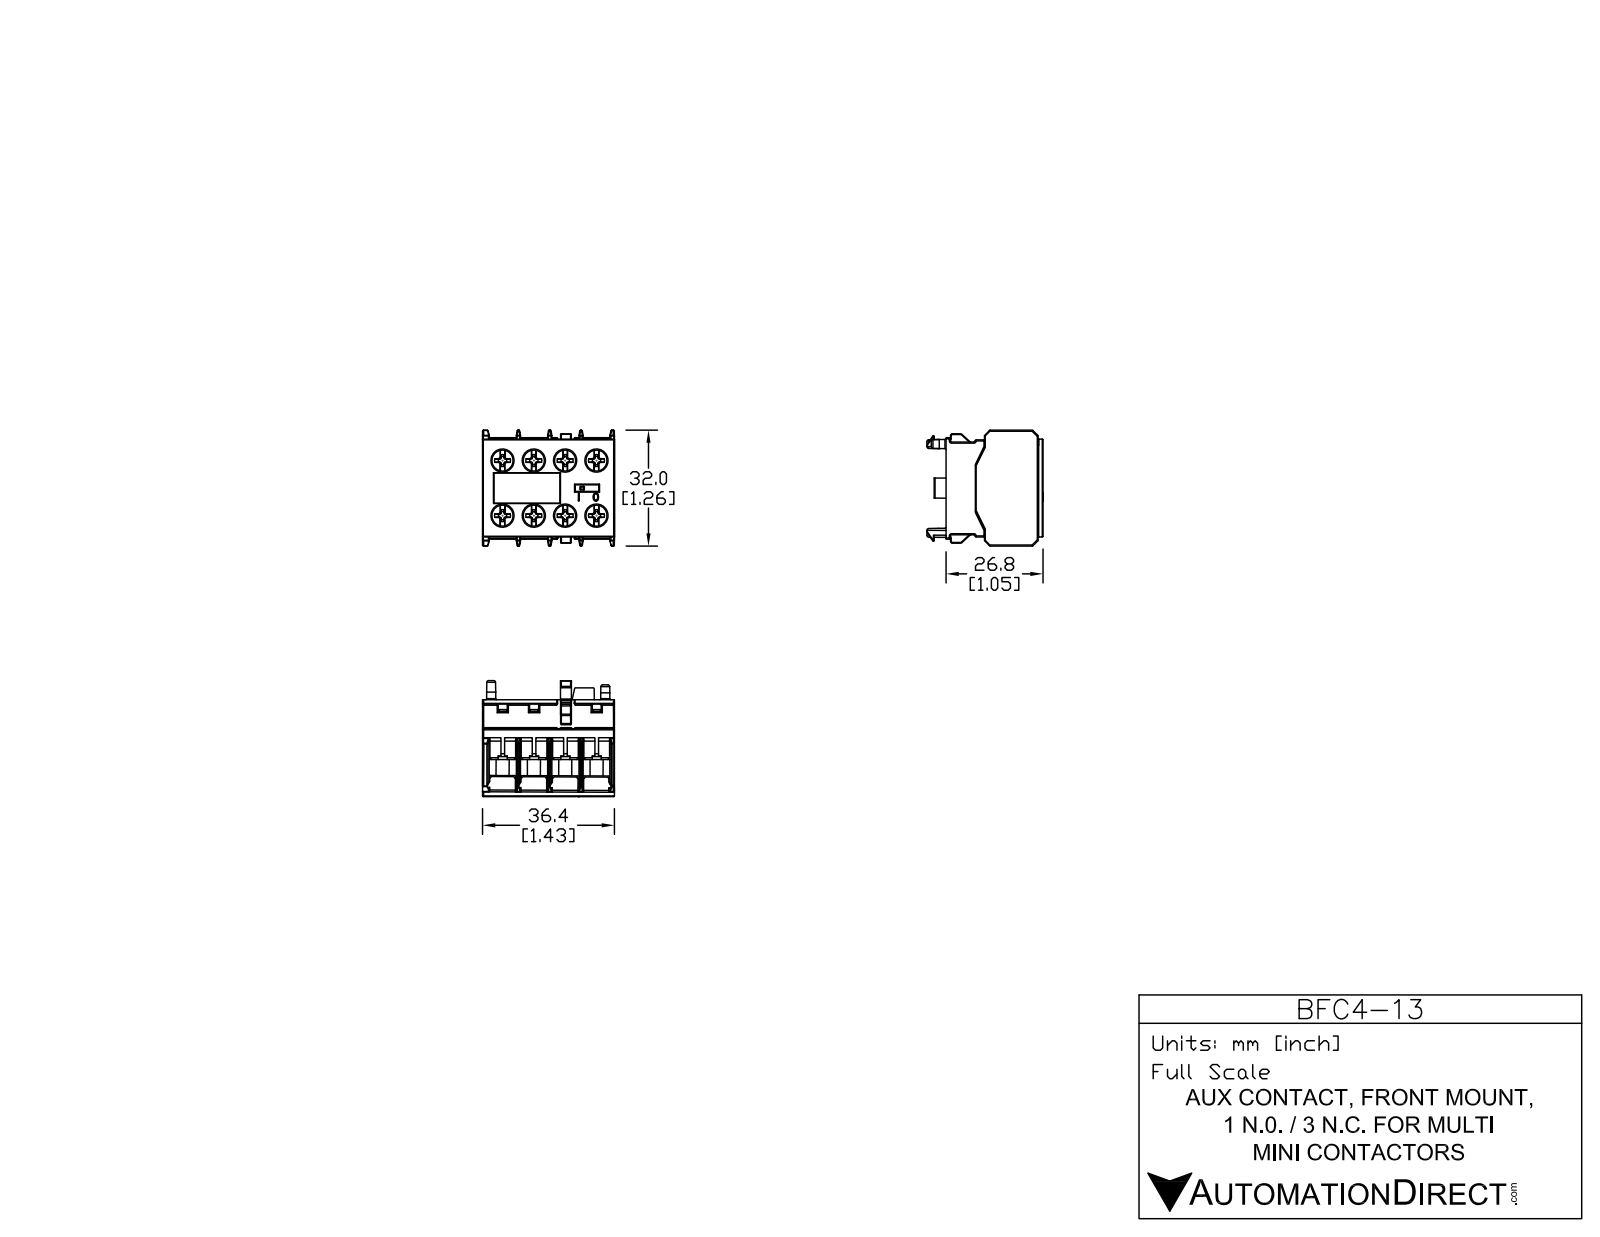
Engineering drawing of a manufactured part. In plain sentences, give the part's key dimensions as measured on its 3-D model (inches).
The part is named "BFC4-13". Its 3-D file was written by "SolidWorks 2013 (AUTOMOTIVE_DESIGN)". It is 20 solids with 761 faces: 593 planar, 168 cylindrical and 0 other. Overall it measures 1.437 by 1.269 by 1.26 inches. Its volume is 1.002 cubic inches and its surface area 26.95 square inches. Round holes: 8 of diameter 0.236. Round bosses or shafts: 8 of diameter 0.197, 8 of diameter 0.118, 3 of diameter 0.108. Partial cylindrical surfaces (rounded edges, fillets, slot ends): 8 of radius 0.02, 8 of radius 0.178, 6 of radius 0.012, 4 of radius 0.01, 2 of radius 0.006, 2 of radius 0.007, 2 of radius 0.008. The main face-to-face distances are 0.049, 0.679, 0.34, 0.63, 0.339, 1.019, 0.291, 0.728, 0.389, 0.29. The hole center spacings are 0.34, 0.591, 0.679, 0.681, 0.9, 0.339, 0.681, 1.019.
